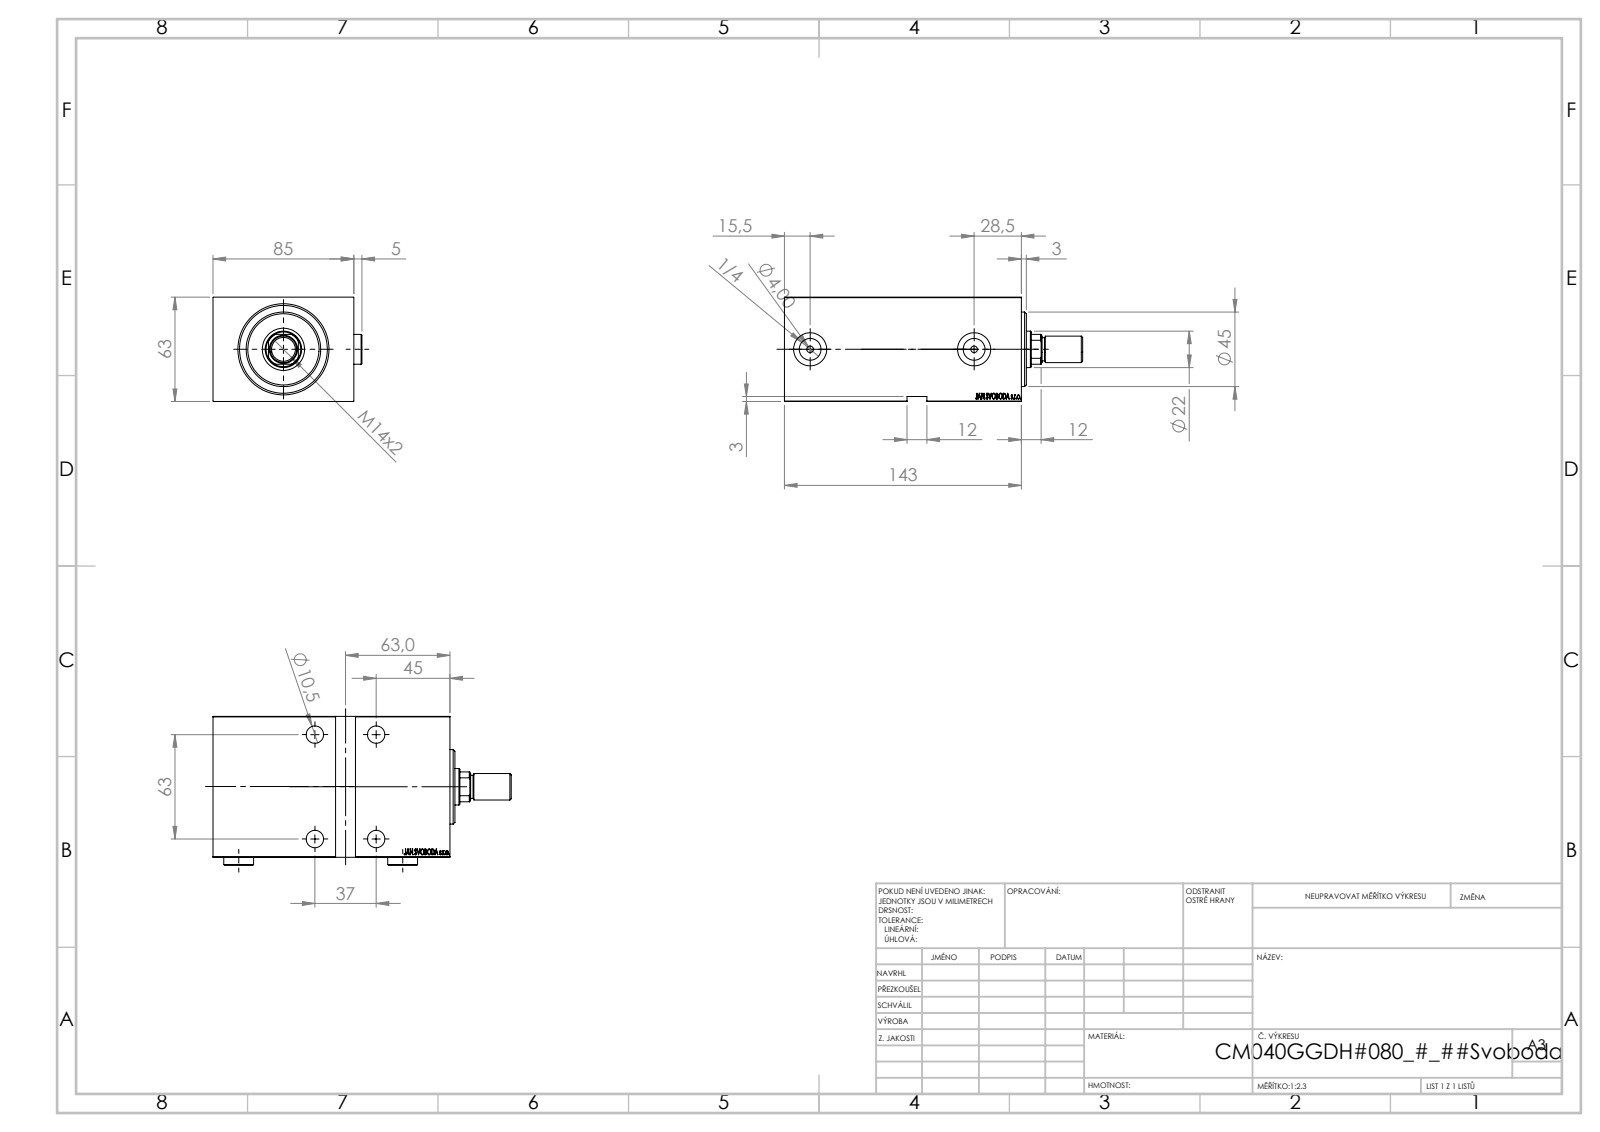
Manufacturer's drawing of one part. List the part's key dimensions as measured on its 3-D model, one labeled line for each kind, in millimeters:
Part name (STEP PRODUCT): V450CM_MALE_METRIC; V450CM_VC_G; Zatka_OIL_PORT; V450CM_G_VCP (+1 more)
STEP written by: SolidWorks 2019 (CONFIG_CONTROL_DESIGN)
Units: millimetres
Bodies: 6 solids, 929 faces (451 planar, 74 cylindrical, 404 other)
Overall size (bounding box): 180 × 89.9 × 63
Volume: 661 009 mm³ · Surface area: 106 773 mm²
Round holes (diameter × count): ⌀10.5 ×4, ⌀16.5 ×4, ⌀4 ×2, ⌀13.16 ×2, ⌀20 ×2, ⌀12.5 ×1, ⌀22 ×1, ⌀25.5 ×1, ⌀40 ×1, ⌀42 ×1, ⌀53 ×1
Round bosses / shafts (diameter × count): ⌀18 ×2, ⌀45 ×1, ⌀27 ×1, ⌀16 ×1, ⌀14 ×1
Partial cylindrical surfaces — rounded edges, fillets, slot ends (radius × count): R10.5 ×1
Main face-to-face distances: 63, 85, 143, 12, 131, 5, 138, 126, 3, 60
Hole centre spacings: 37, 63, 73.06, 99
